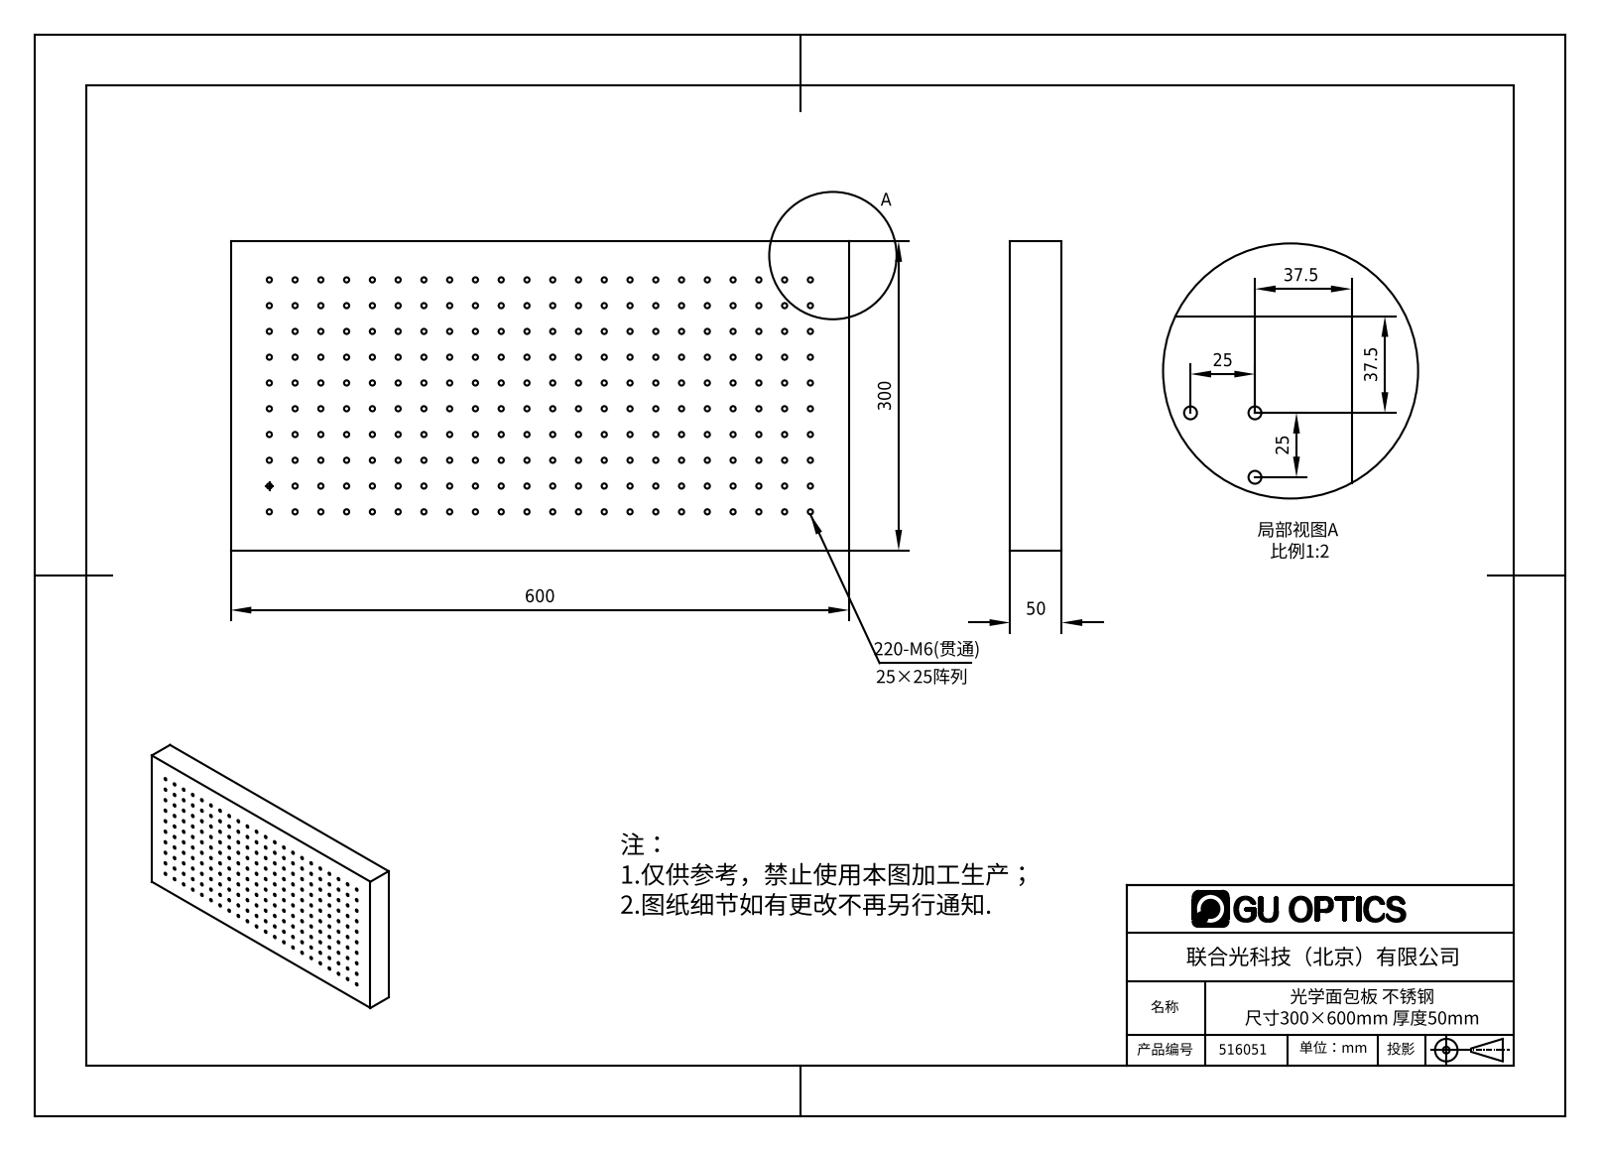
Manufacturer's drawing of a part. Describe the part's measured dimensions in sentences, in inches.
The part is named "516051". Its 3-D file was written by "SolidWorks 2016 (AUTOMOTIVE_DESIGN)". It is 1 solid with 446 faces: 6 planar, 440 cylindrical and 0 other. Overall it measures 23.622 by 11.811 by 1.969 inches. Its volume is 536 cubic inches and its surface area 951.9 square inches. Round holes: 220 of diameter 0.197. The main face-to-face distances are 1.969, 11.811, 23.622. The hole center spacings are 2.201, 0.984, 1.392, 3.113, 1.969, 3.549, 4.058, 2.953.
